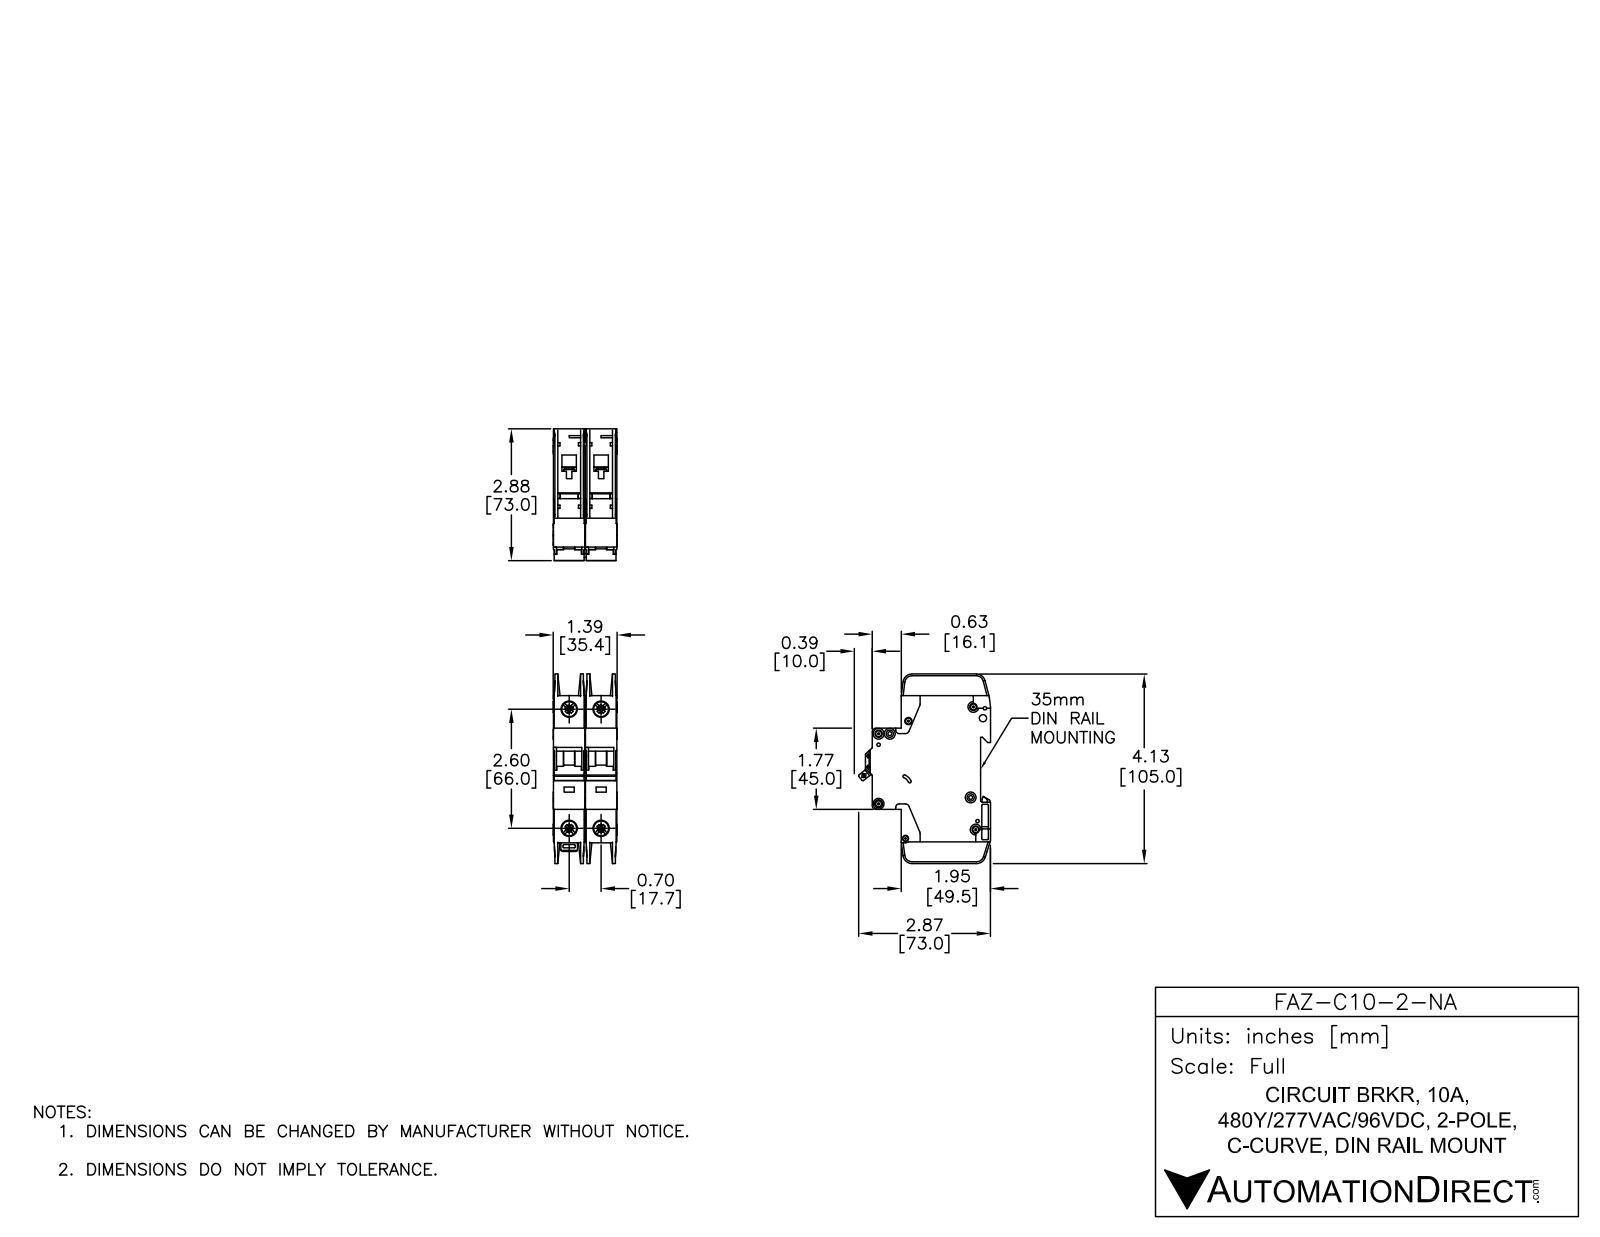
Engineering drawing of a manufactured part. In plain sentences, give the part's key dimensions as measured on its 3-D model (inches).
The part is named "FAZ-C10-2-NA". Its 3-D file was written by "SolidWorks 2014 (AUTOMOTIVE_DESIGN)". It is 6 solids with 1568 faces: 818 planar, 526 cylindrical and 224 other. Overall it measures 4.134 by 2.876 by 1.394 inches. Its volume is 9.482 cubic inches and its surface area 76.69 square inches. Round holes: 7 of diameter 0.142, 4 of diameter 0.281, 4 of diameter 0.323, 2 of diameter 0.043, 2 of diameter 0.059, 2 of diameter 0.157, 1 of diameter 0.075, 1 of diameter 0.085, 1 of diameter 0.087, 1 of diameter 0.1, 1 of diameter 0.13, 1 of diameter 0.134. Round bosses or shafts: 7 of diameter 0.236, 2 of diameter 0.098. Partial cylindrical surfaces (rounded edges, fillets, slot ends): 47 of radius 0.01, 24 of radius 0.02, 18 of radius 0.039, 12 of radius 0.079, 5 of radius 0.197, 4 of radius 0.071, 4 of radius 0.157, 2 of radius 0.008. The main face-to-face distances are 0.697, 0.689, 0.028, 0.593, 0.096, 0.069, 0.62, 0.524, 1.386, 0.669. The hole center spacings are 0.244, 0.697, 2.598, 2.69, 0.204, 0.24, 0.322, 0.337.
